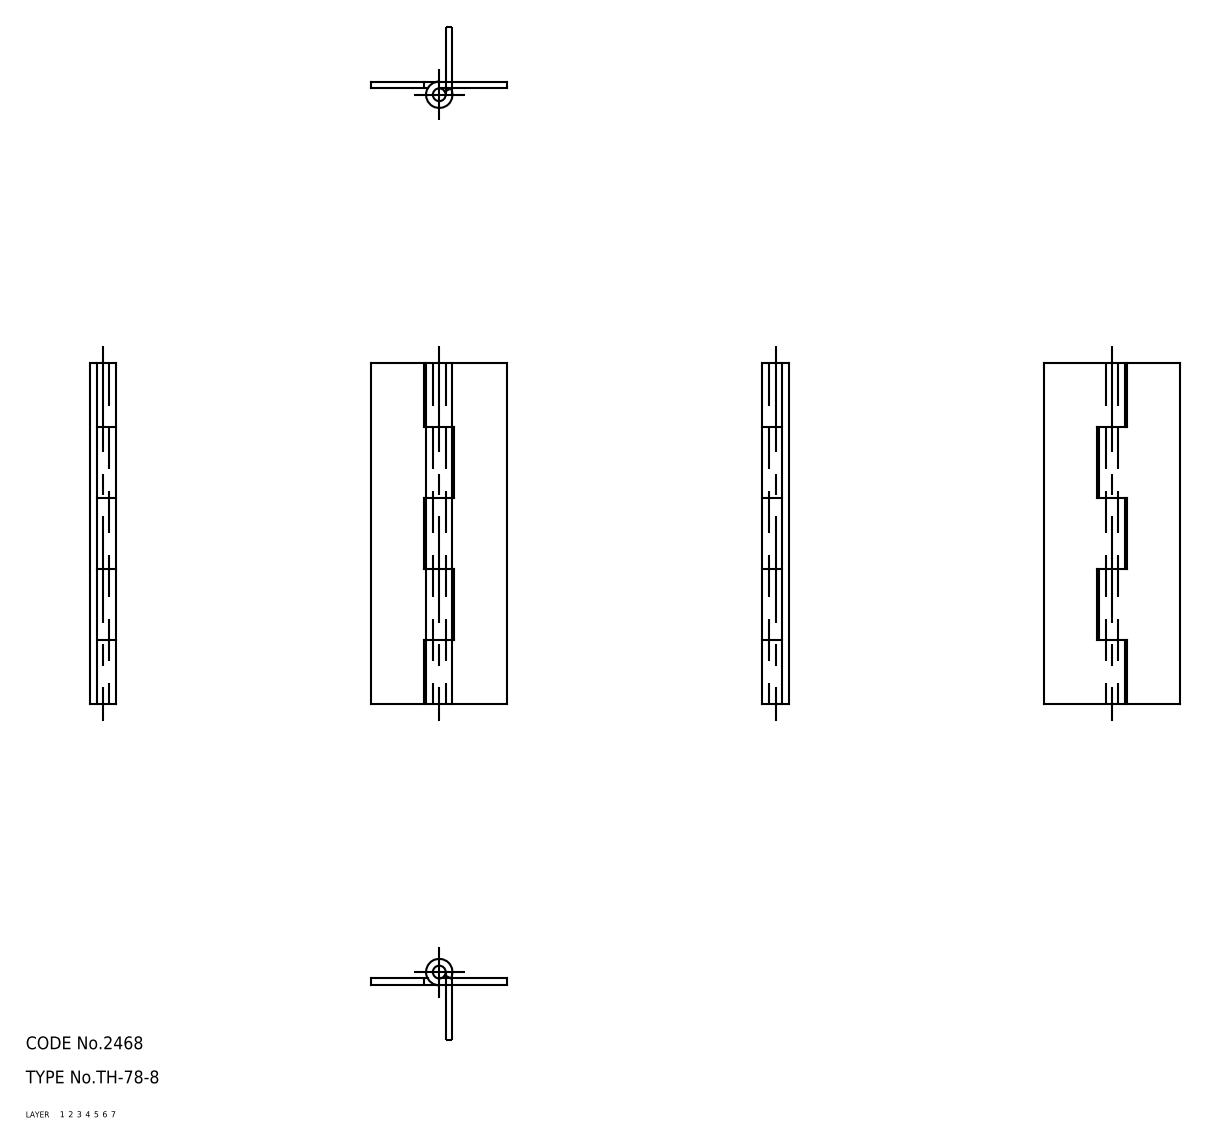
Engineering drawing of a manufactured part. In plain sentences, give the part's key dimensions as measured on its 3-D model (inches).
The part is named "hinge piece_B; hinge piece_A; shaft; TH_78_8_16925_36". Its 3-D file was written by "CADfix (AUTOMOTIVE_DESIGN)". It is 3 solids with 42 faces: 0 planar, 0 cylindrical and 42 other. Overall it measures 3.15 by 1.26 by 0.244 inches. Its volume is 0.351 cubic inches and its surface area 12.53 square inches.
